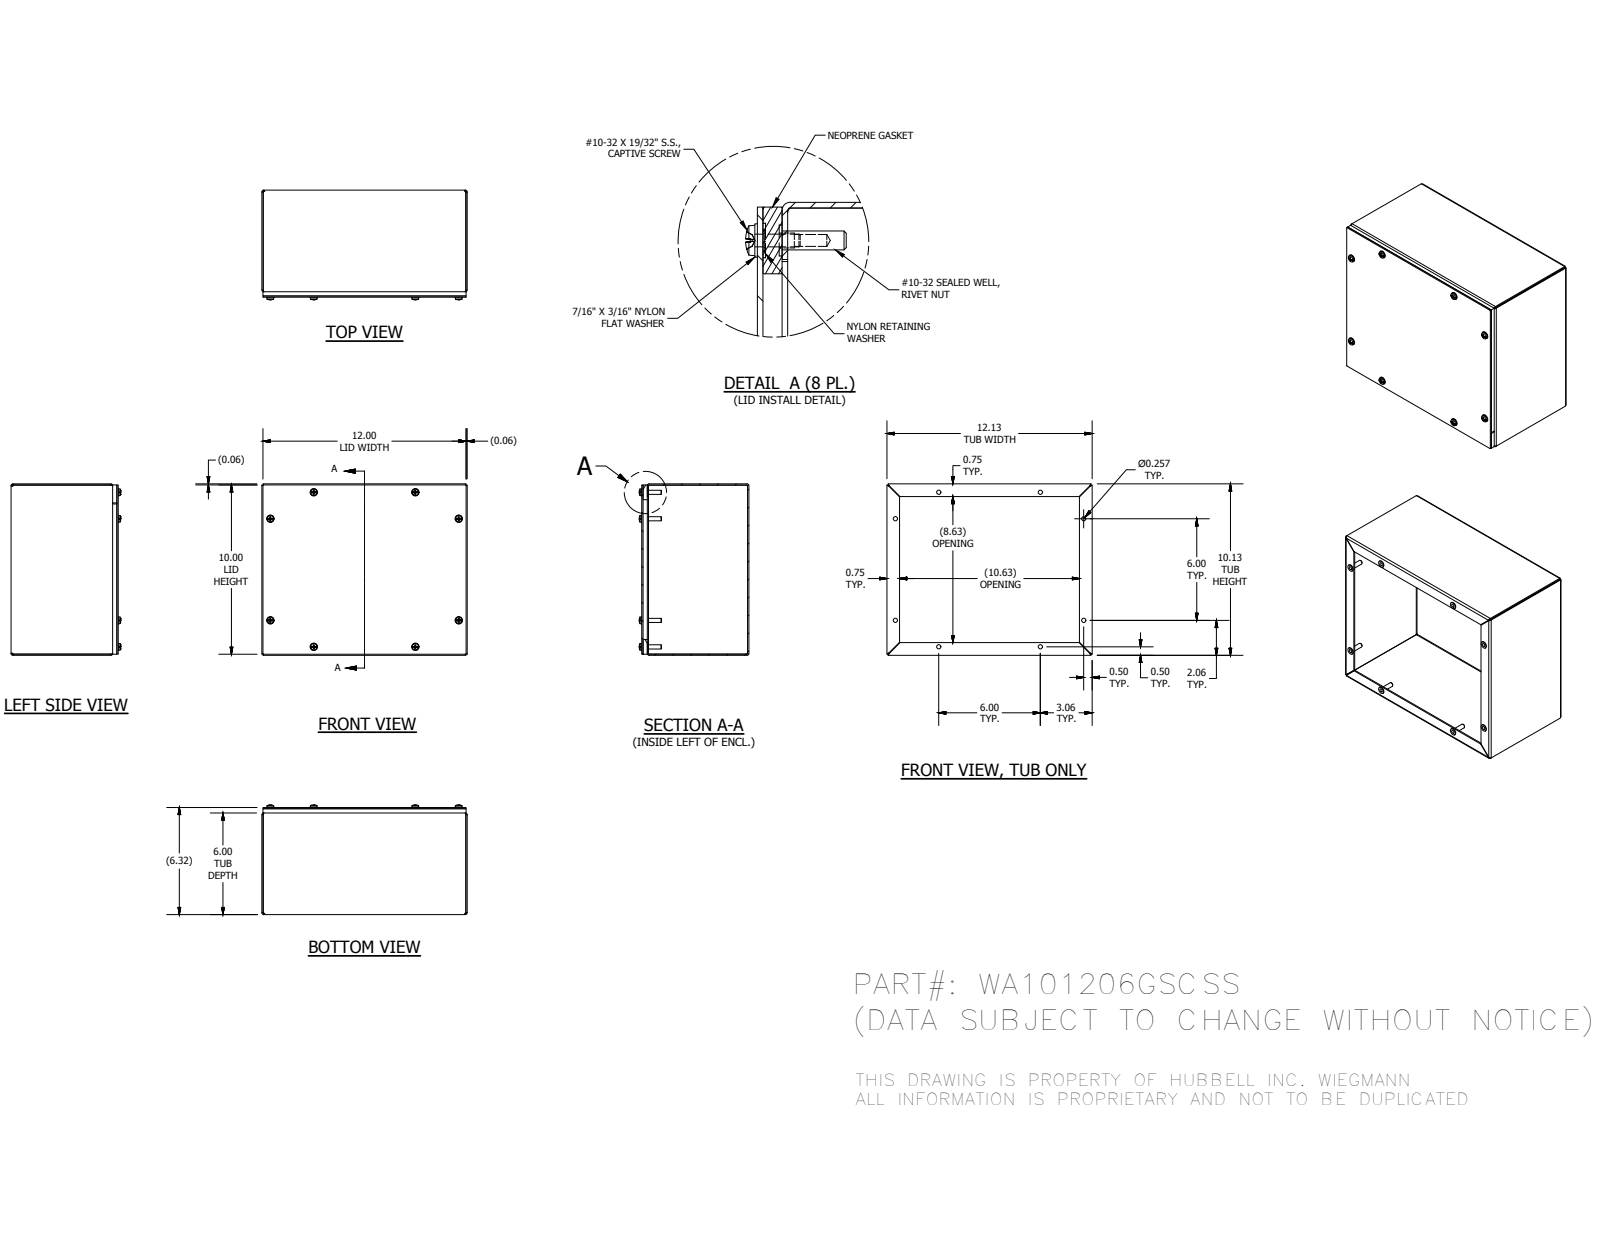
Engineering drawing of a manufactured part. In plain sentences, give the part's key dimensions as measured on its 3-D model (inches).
The part is named "WA101206GSCSSBKP; WA1012GSCSSLID; 316281; 37210 (+4 more)". Its 3-D file was written by "Autodesk Inventor 2016 (AUTOMOTIVE_DESIGN)". It is 36 solids with 764 faces: 420 planar, 160 cylindrical and 184 other. Overall it measures 12.125 by 10.125 by 6.479 inches. Its volume is 48.23 cubic inches and its surface area 1 180 square inches. Round holes: 8 of diameter 0.156, 8 of diameter 0.188, 8 of diameter 0.196, 8 of diameter 0.257, 8 of diameter 0.278, 8 of diameter 0.281, 8 of diameter 0.313. Round bosses or shafts: 8 of diameter 0.453, 8 of diameter 0.437, 8 of diameter 0.406, 8 of diameter 0.248, 8 of diameter 0.167. Partial cylindrical surfaces (rounded edges, fillets, slot ends): 12 of radius 0.031, 8 of radius 0.07, 8 of radius 0.089, 8 of radius 0.105. The main face-to-face distances are 0.074, 6.25, 10.051, 6.324, 6.176, 12.051, 5.926, 0.324, 10.125, 9.977. The hole center spacings are 6, 8.703, 8.704, 11.424, 3, 3.001, 3.001, 3.002.
